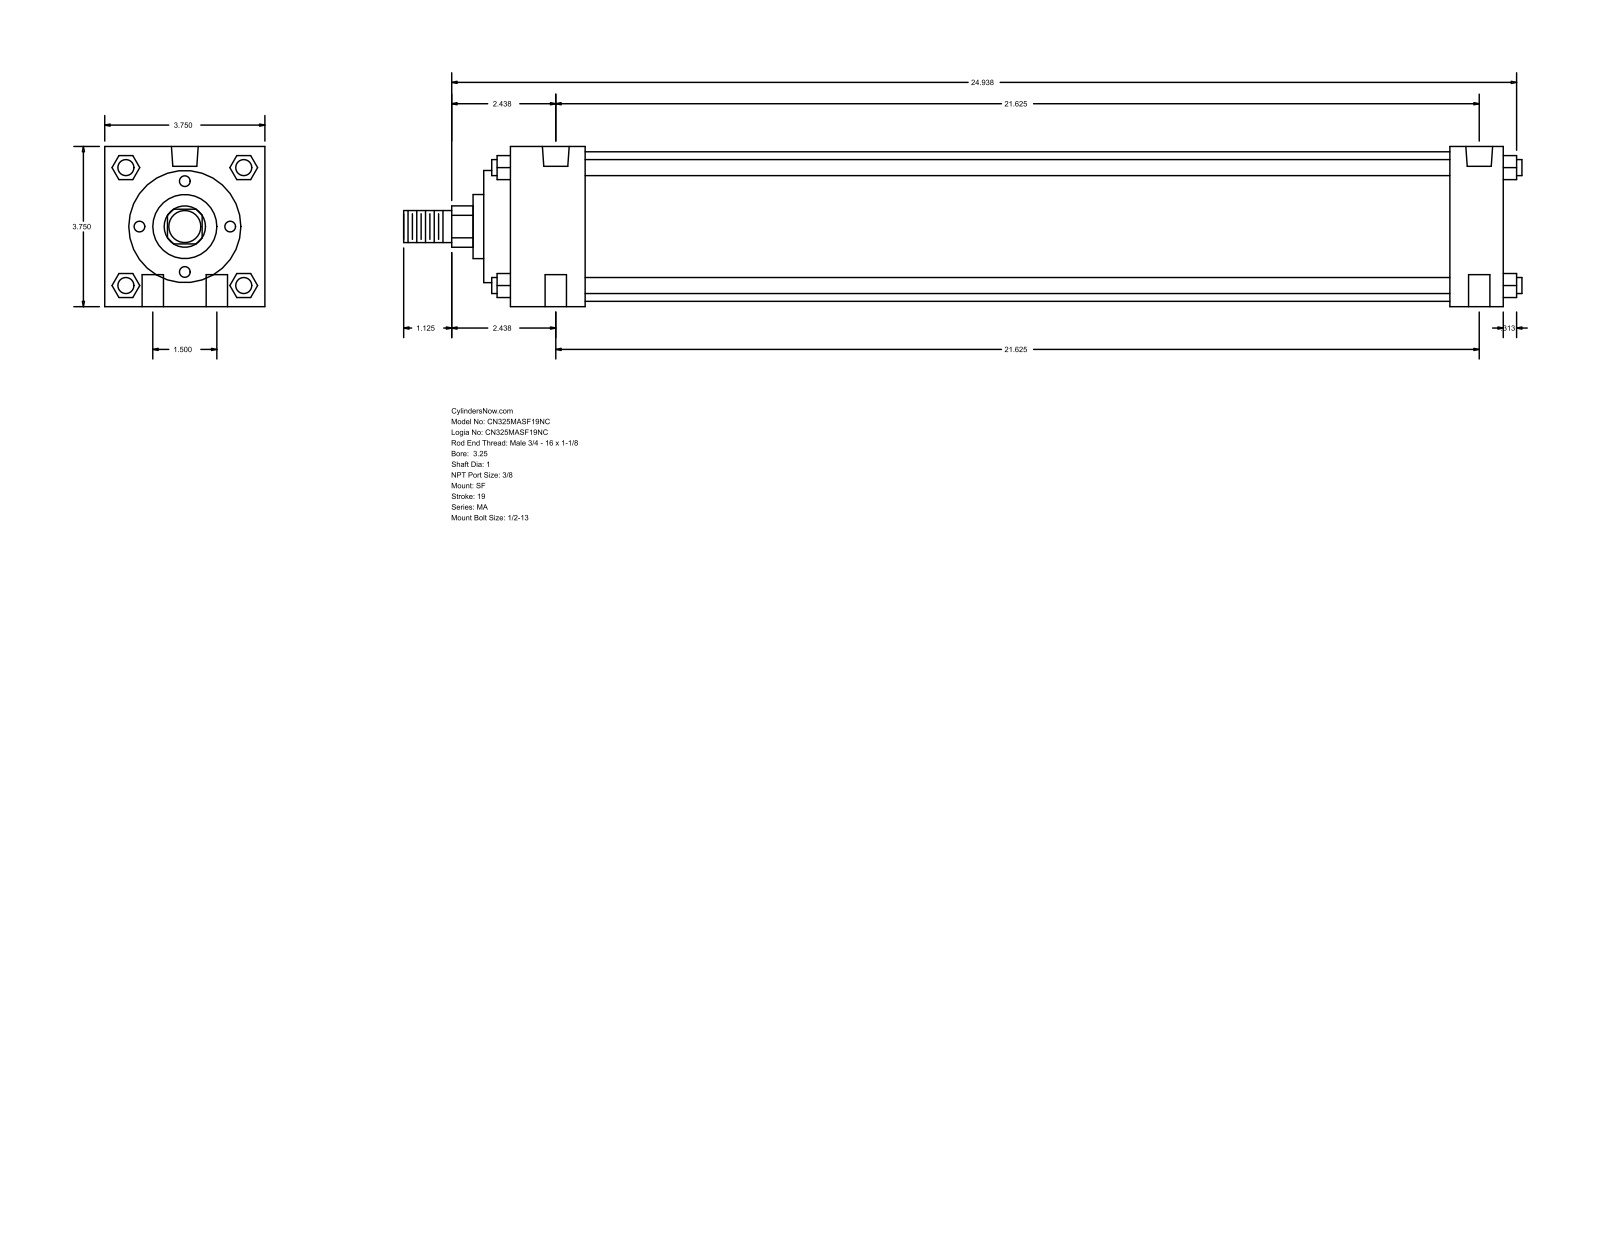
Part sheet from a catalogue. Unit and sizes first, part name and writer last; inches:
Units: inches
Overall size (bounding box): 26.187 × 3.75 × 3.75
Round holes (diameter × count): ⌀0.5 ×4, ⌀0.437 ×2, ⌀0.627 ×2
Round bosses / shafts (diameter × count): ⌀0.375 ×4, ⌀3.5 ×1, ⌀2.625 ×1, ⌀1.5 ×1, ⌀1 ×1, ⌀0.75 ×1
Partial cylindrical surfaces — rounded edges, fillets, slot ends (radius × count): R0.484 ×1
Main face-to-face distances: 3.75, 23.25, 22, 1.25, 1.75, 20.25, 21.5, 0.625, 2.375, 22.625
Hole centre spacings: 0.75, 21.638, 21.625, 1.5, 21.677, 21.25
Bodies: 0 solids, 126 faces (95 planar, 31 cylindrical, 0 other)
Part name (STEP PRODUCT): MA_SF__0325_1
STEP written by: GSSL Pune (CONFIG_CONTROL_DESIGN)
